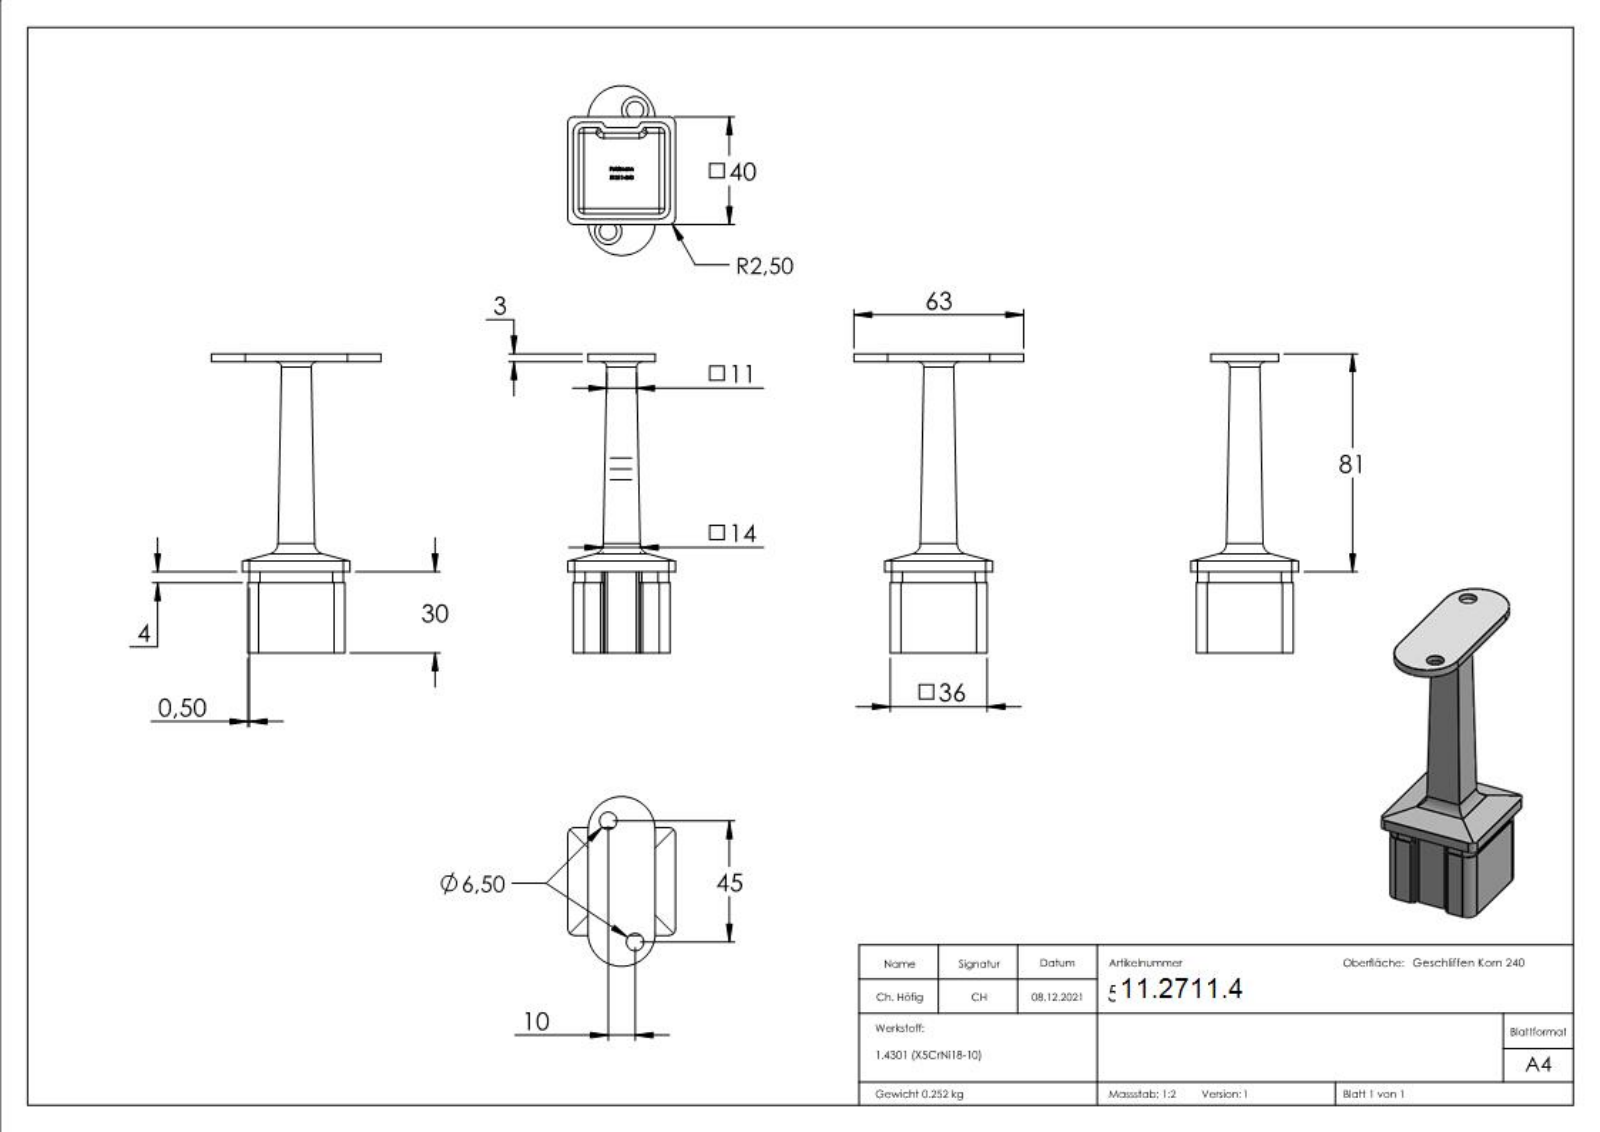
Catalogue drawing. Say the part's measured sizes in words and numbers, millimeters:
The part is named "51211-240". Its 3-D file was written by "SolidWorks 2018 (CONFIG_CONTROL_DESIGN)". It is 1 solid with 305 faces: 172 planar, 48 cylindrical and 85 other. Overall it measures 111 by 63 by 40 millimeters. Its volume is 31 945 cubic millimeters and its surface area 18 290 square millimeters. Round holes: 2 of diameter 6.5, 2 of diameter 10. Partial cylindrical surfaces (rounded edges, fillets, slot ends): 15 of radius 2, 12 of radius 4, 10 of radius 1, 4 of radius 2.5, 2 of radius 12.5. The main face-to-face distances are 2, 34, 32, 36, 81, 78, 3, 4, 30, 38. The hole center spacings are 46.1.
